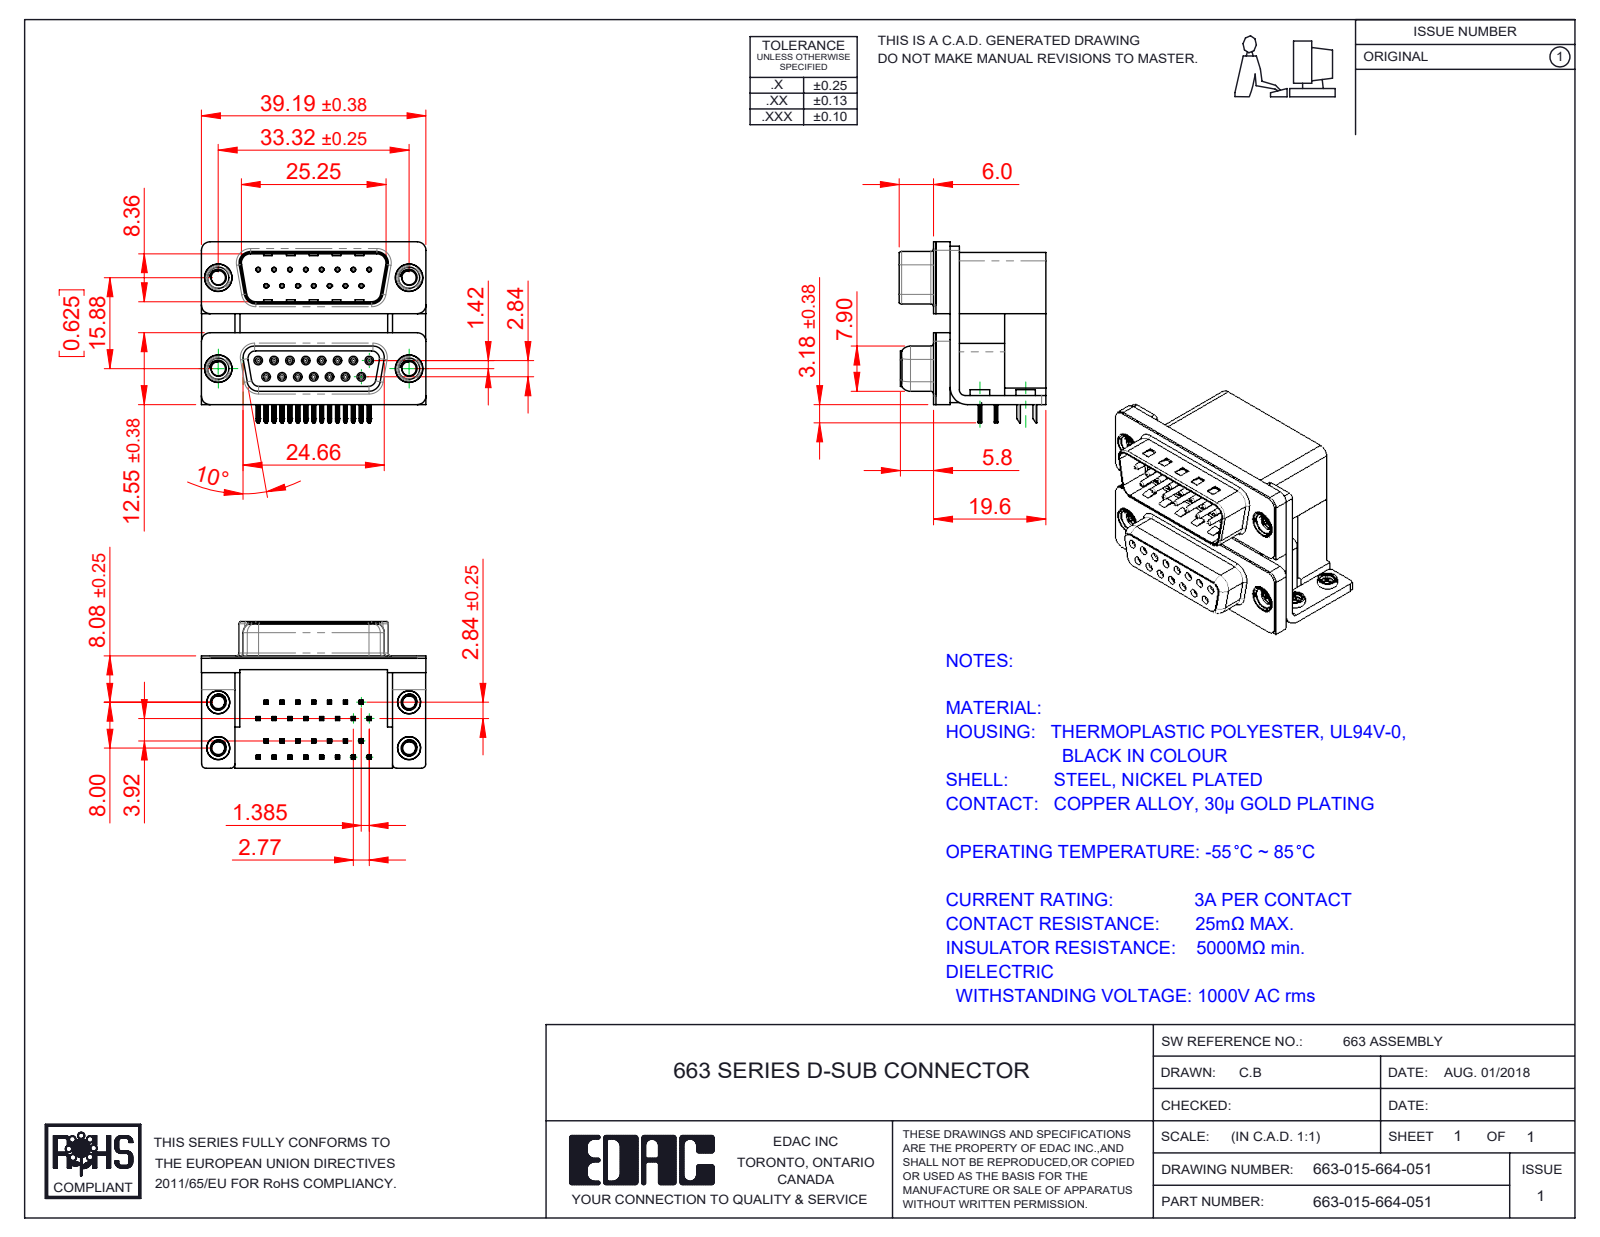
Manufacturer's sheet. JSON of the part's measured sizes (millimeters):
{"part_name": "663 Housing Lower_15 Contacts; 663 Housing Upper_15 Contacts L; 663 Shell Receptacle_15 Contacts; 663 Housing Spacer_15 Contacts L (+8 more)", "step_written_by": "SolidWorks 2020 (CONFIG_CONTROL_DESIGN)", "units": "millimeters", "bodies": {"solids": 45, "faces": 4056, "planar": 2027, "cylindrical": 1098, "other": 931}, "overall_size": [39.19, 31.61, 25.6], "volume_mm3": 14616, "surface_area_mm2": 16419, "round_holes": [[0.8, 30], [0.35, 15], [0.9, 15], [2.26, 4], [2.5, 4], [2.75, 4], [3.2, 4], [3.5, 4], [4, 4], [4.8, 4], [5, 4]], "round_bosses_or_shafts": [[1.2, 15], [0.75, 15], [4.9, 4], [4.75, 4], [4, 4], [3.9, 4], [3.4, 4]], "partial_cylinders_radius": [[0.1, 120], [0.15, 60], [0.25, 60], [0.12, 30], [0.35, 30], [1.5, 16], [0.34, 15], [0.5, 12]], "face_to_face_distances": [0.4, 19.2, 16.7, 2.5, 10.7, 7.2, 12, 9.5, 2.9, 19.6], "hole_center_spacings": [3.16, 16.12, 2.77, 16.82, 5.54, 8.31, 15.88, 17.92]}
